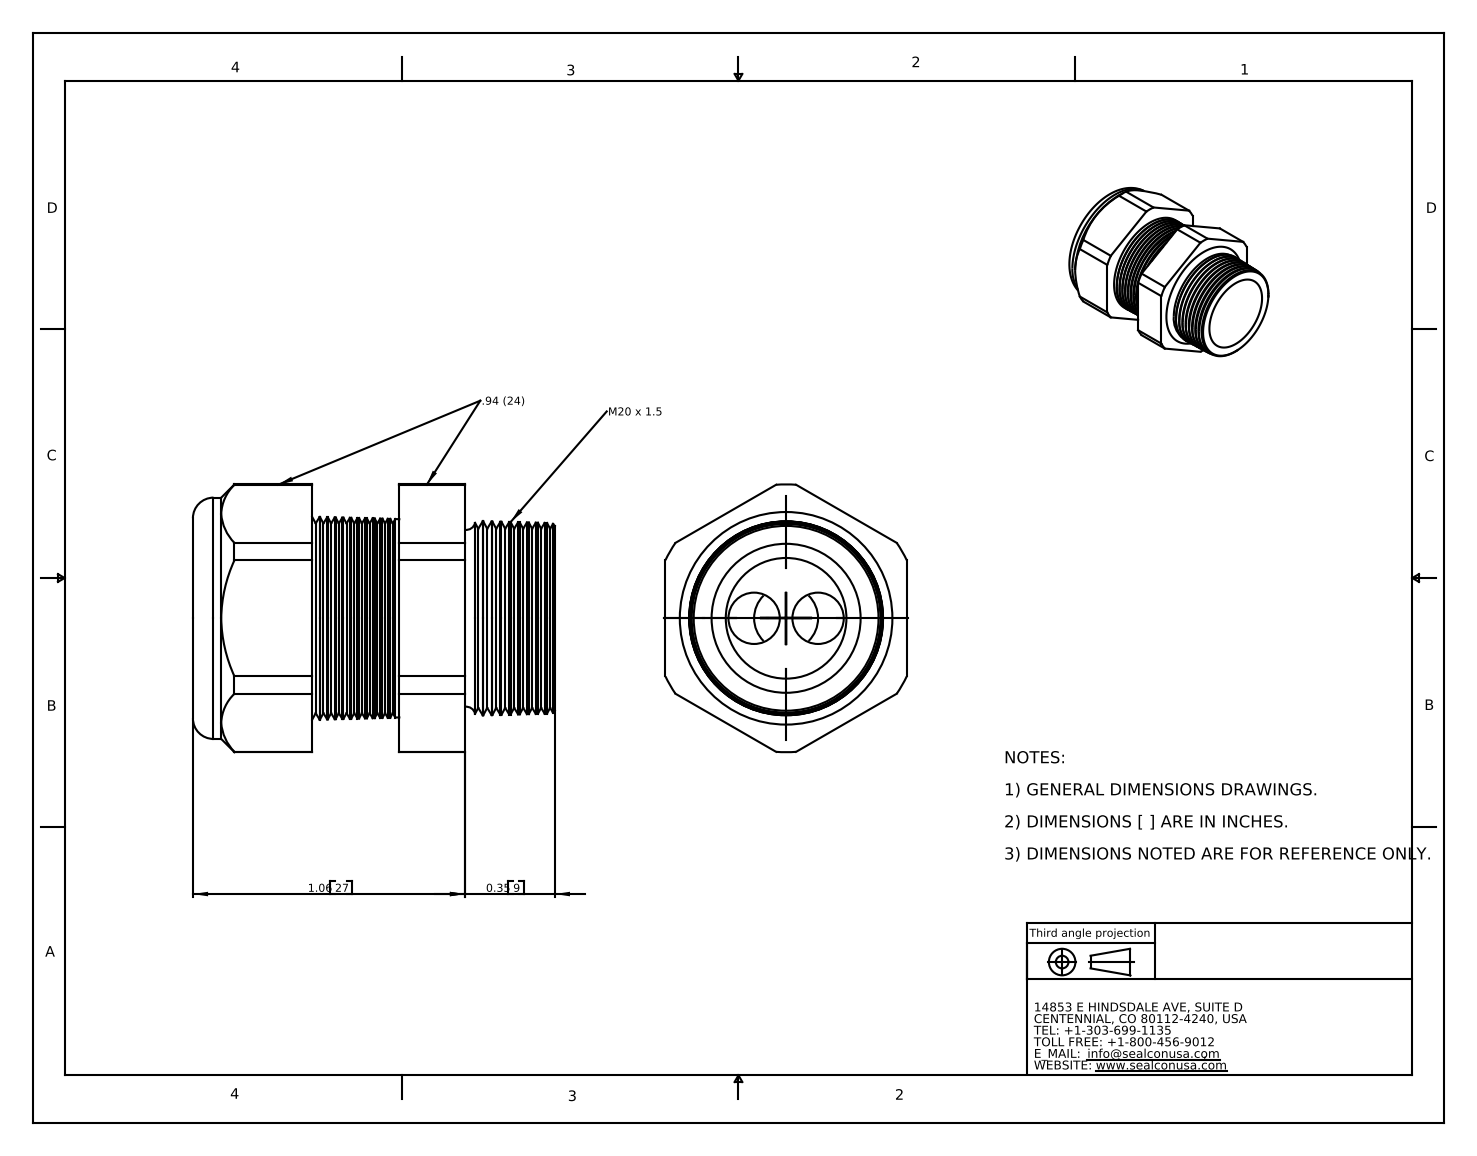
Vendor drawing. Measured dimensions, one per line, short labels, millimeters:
name: CD20M4-BK
written by: SolidWorks 2007 (CONFIG_CONTROL_DESIGN)
unit: mm
bodies: 2 solids, 178 faces (20 planar, 24 cylindrical, 134 other)
size: 35.8 × 26.5 × 23.9
volume: 9 360 mm³; area: 6 390 mm²
holes: 2× ⌀5.1, 1× ⌀11.4, 1× ⌀11.9
bosses: 1× ⌀23.9
rounds: 1× R13.3
face distances: 23.9, 20.4, 11.8, 8.6, 26.9, 15.1, 6.5, 35.8, 24, 15.4
hole spacings: 3.1, 6.3
